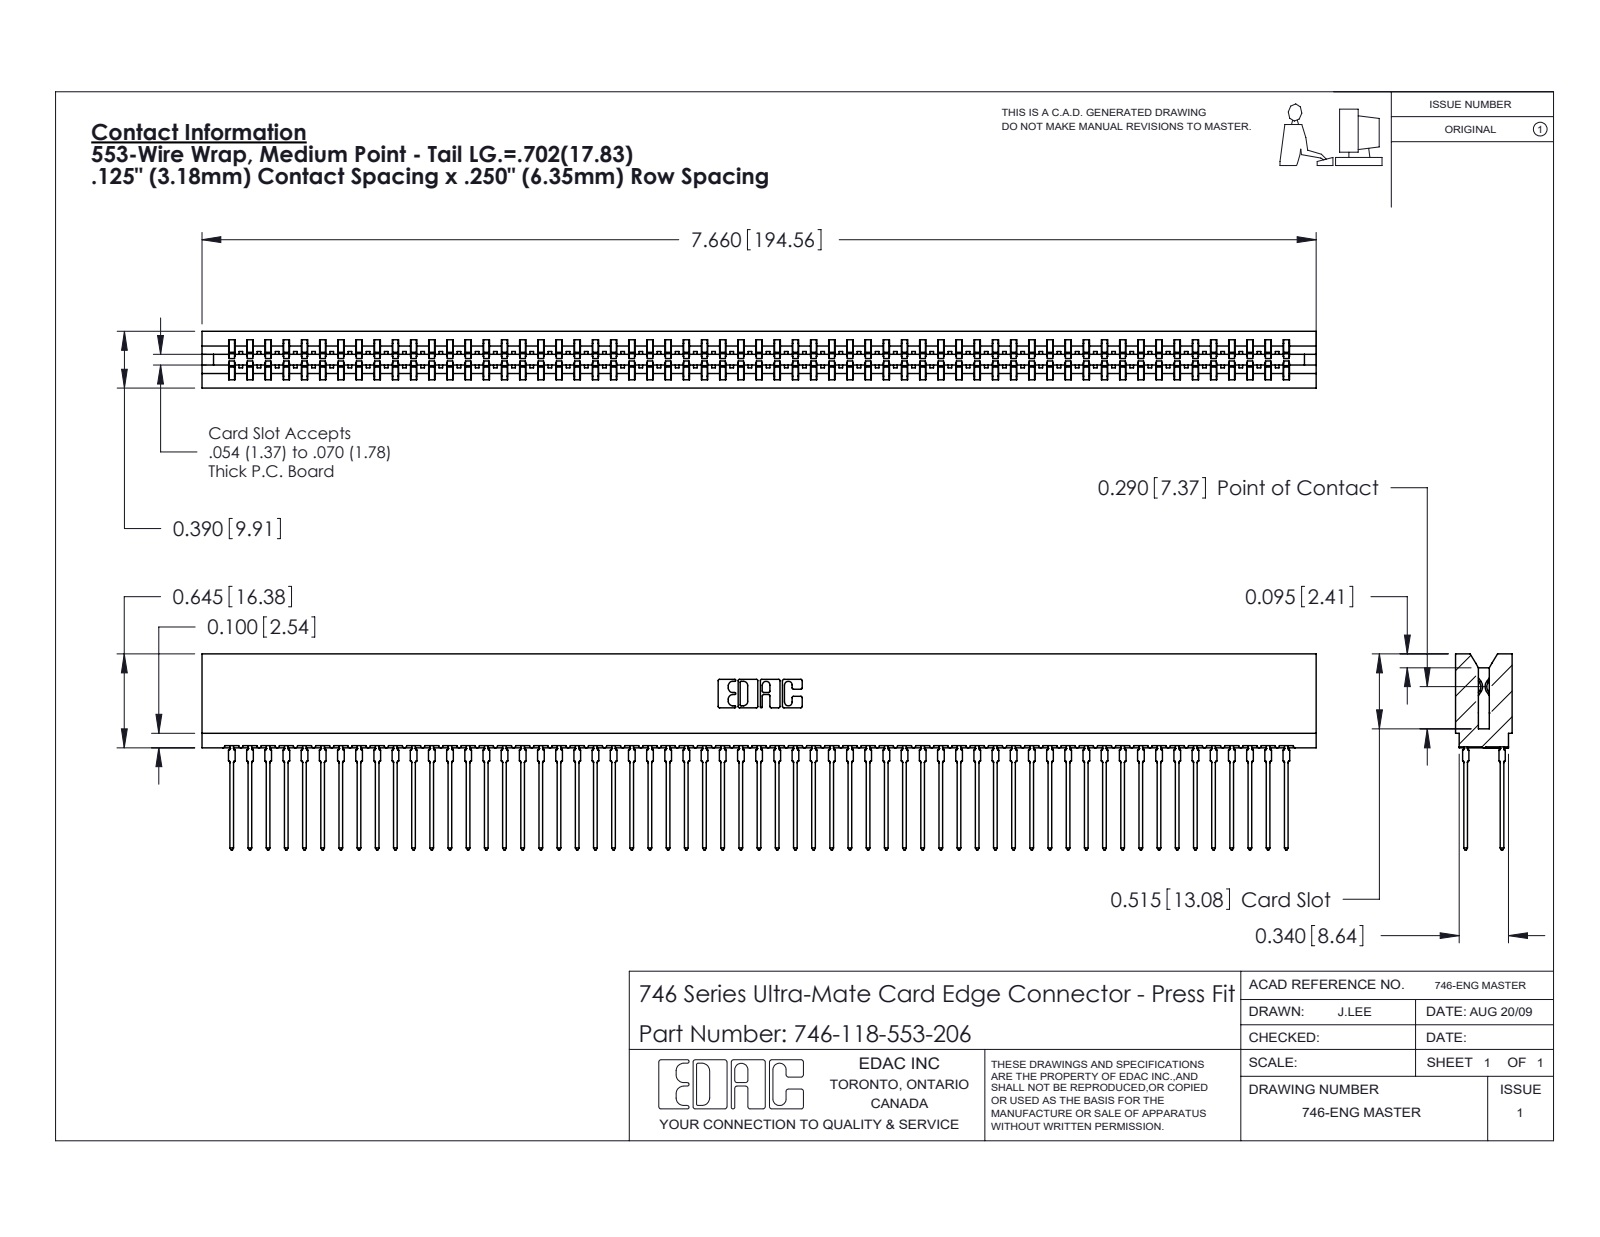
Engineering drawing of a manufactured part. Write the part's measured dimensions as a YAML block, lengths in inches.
part_name: "746-118-553-206; 746-292-001_553; 746 Part_.515 Slot Depth - 06"
step_written_by: "SolidWorks 2020 (CONFIG_CONTROL_DESIGN)"
units: inches
bodies: {solids: 119, faces: 10659, planar: 5484, cylindrical: 2107, other: 3068}
overall_size: [7.66, 1.346, 0.39]
volume: 1.297
surface_area: 57.16
partial_cylinders:
  - {radius: 0.021, count: 236}
  - {radius: 0.015, count: 60}
  - {radius: 0.01, count: 22}
  - {radius: 0.005, count: 8}
  - {radius: 0.011, count: 8}
  - {radius: 0.007, count: 6}
  - {radius: 0.031, count: 6}
  - {radius: 0.026, count: 3}
face_to_face_distances: [0.057, 0.333, 0.25, 0.025, 0.307, 0.39, 0.083, 0.275, 0.174, 0.158]
